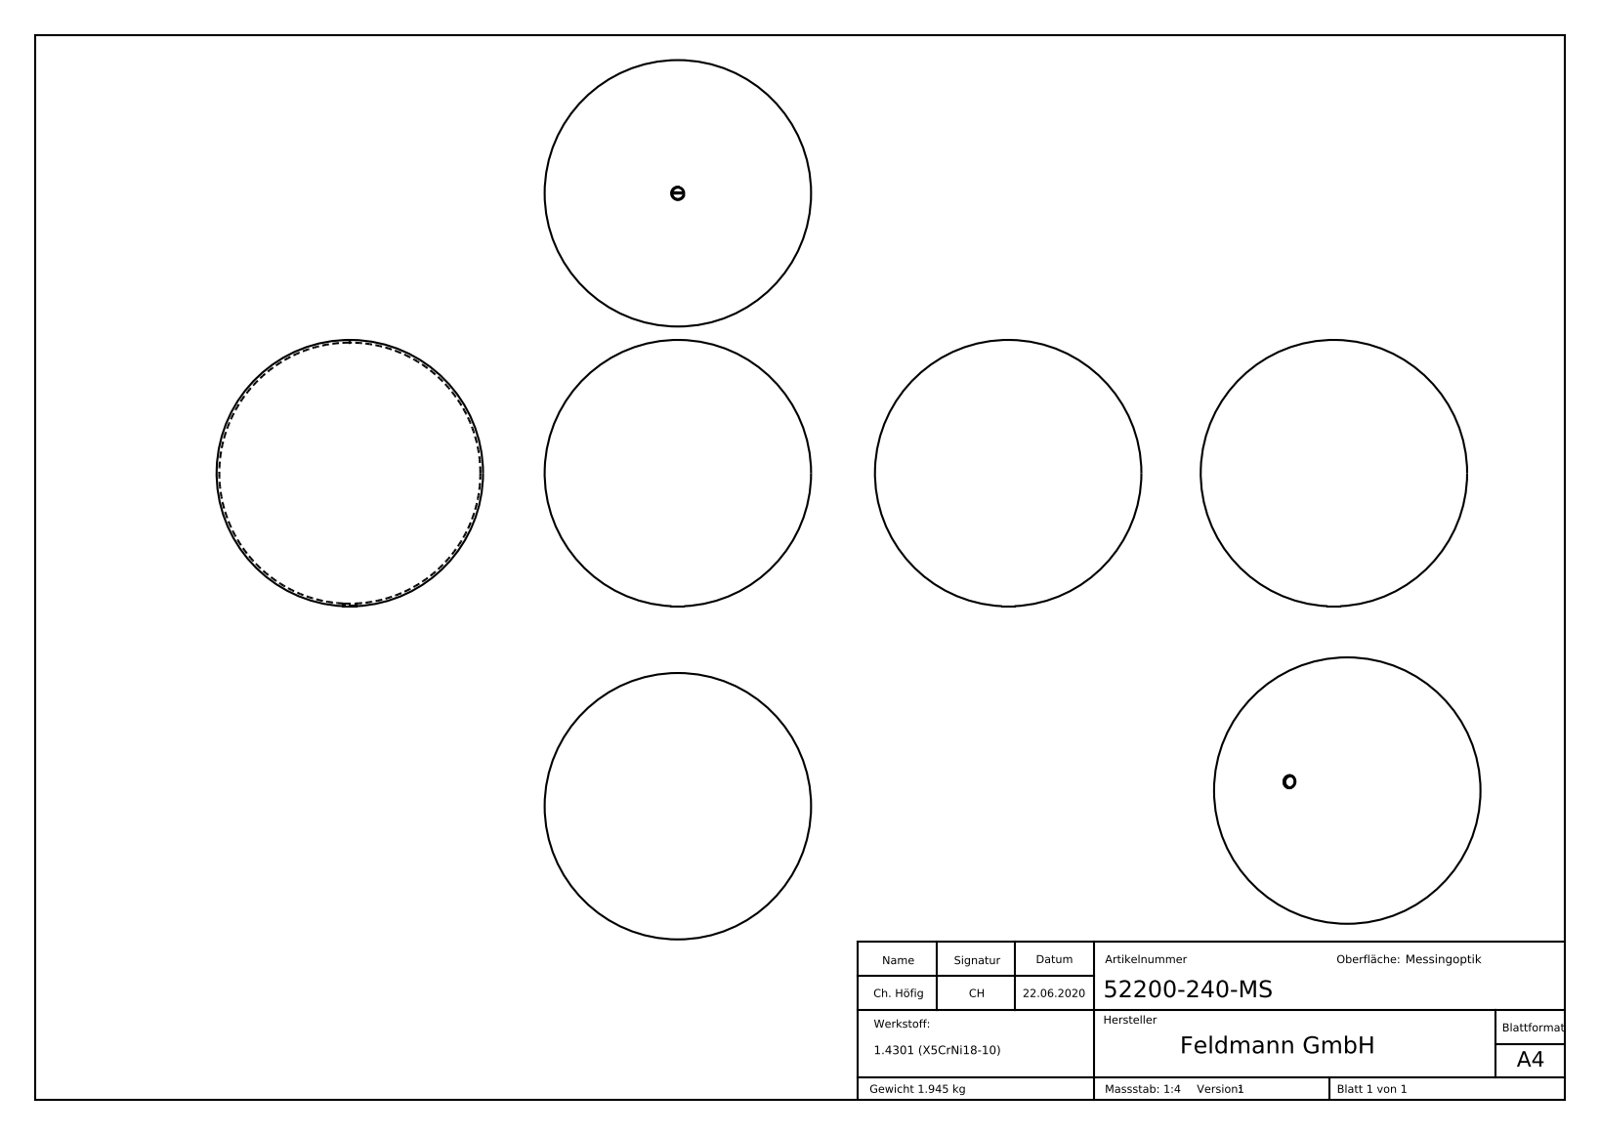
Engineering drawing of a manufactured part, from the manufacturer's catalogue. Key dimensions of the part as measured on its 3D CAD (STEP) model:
Part name (STEP PRODUCT): 52200-240-MS
STEP written by: SolidWorks 2015 (CONFIG_CONTROL_DESIGN)
Units: millimetres
Bodies: 1 solid, 261 faces (114 planar, 1 cylindrical, 146 other)
Overall size (bounding box): 200 × 200 × 199.89
Volume: 246 217 mm³ · Surface area: 246 288 mm²
Round holes (diameter × count): ⌀8.5 ×1
Main face-to-face distances: 1.12, 0.45, 0.33, 0.76, 0.5, 0.43, 0.62, 5.05, 1.34, 0.52
